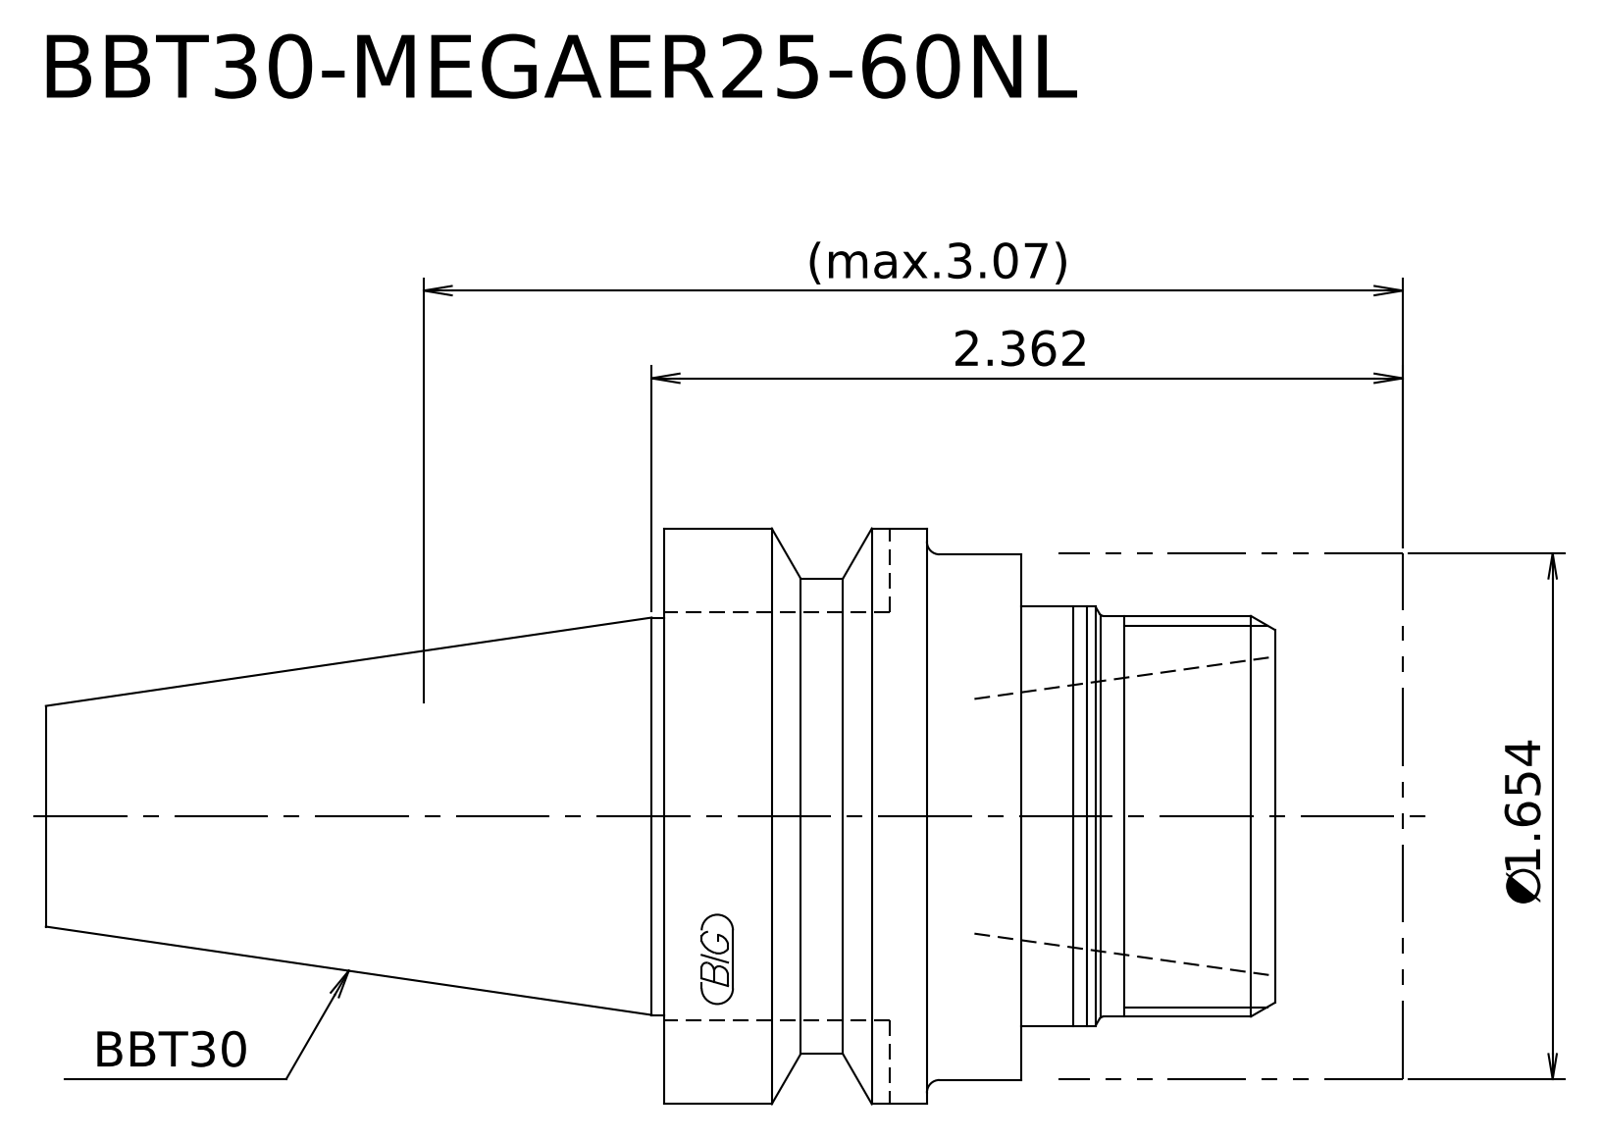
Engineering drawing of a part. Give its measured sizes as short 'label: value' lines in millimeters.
written by: Kubotek KeyCreator 2011 V10.0.2 (22737) (automotive_design)
unit: mm
bodies: 2 solids, 21 faces (7 planar, 8 cylindrical, 6 other)
size: 108.4 × 46 × 46
volume: 121 642 mm³; area: 19 434 mm²
bosses: 1× ⌀46, 1× ⌀42, 1× ⌀41.85, 1× ⌀38, 1× ⌀33.5, 1× ⌀32, 1× ⌀31.75
face distances: 27.5, 59, 31.5, 10.2, 17.3, 48.8, 30.5, 20.3, 3, 28.5
